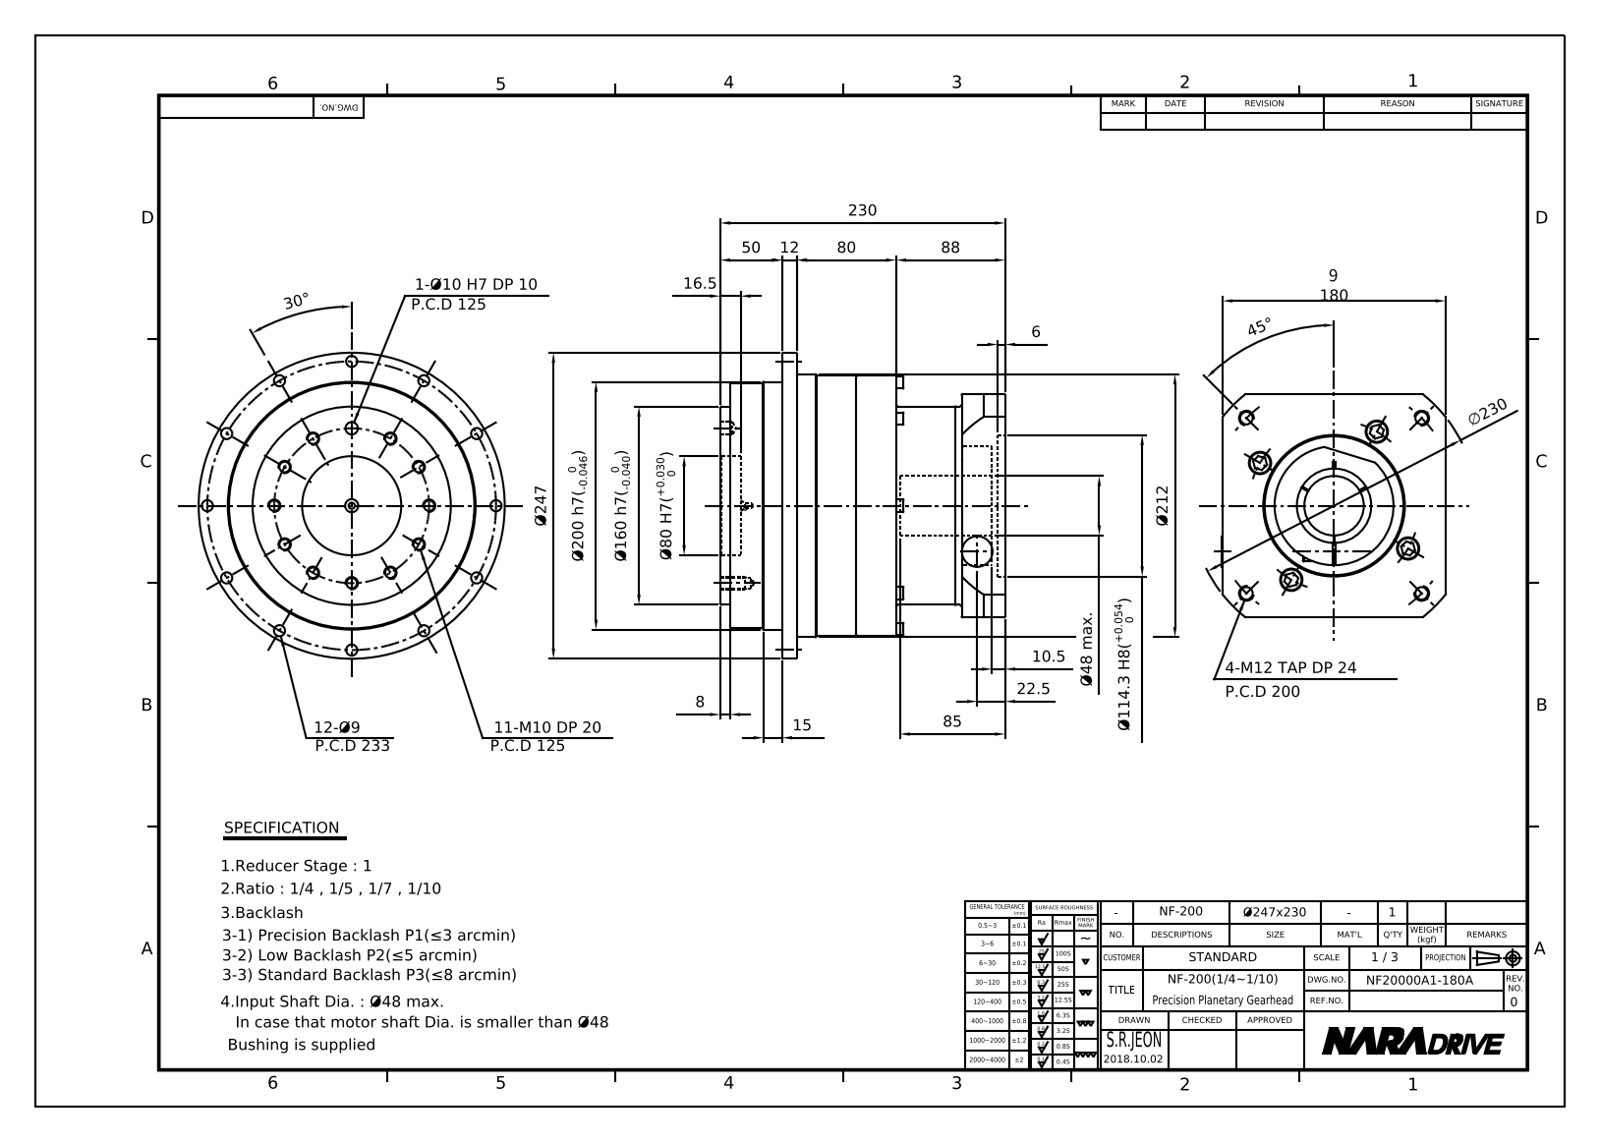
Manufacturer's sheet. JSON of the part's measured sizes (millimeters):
{"part_name": "NF20000A1-180A", "step_written_by": "Autodesk Inventor 2015 (AUTOMOTIVE_DESIGN)", "units": "millimeters", "bodies": {"solids": 1, "faces": 436, "planar": 186, "cylindrical": 127, "other": 123}, "overall_size": [247, 247, 230], "volume_mm3": 5312000, "surface_area_mm2": 463081, "round_holes": [[8.38, 12], [9, 12], [4.92, 8], [6.5, 8], [10.11, 8], [14, 4], [20, 4], [10, 1], [11, 1], [12.5, 1], [14.5, 1], [48, 1]], "round_bosses_or_shafts": [[10, 9], [6, 8], [18, 4], [12, 4], [247, 1], [212, 1], [210, 1], [200, 1]], "partial_cylinders_radius": [[2, 4], [9, 1], [115, 1]], "face_to_face_distances": [180, 43, 134, 179, 120, 85, 25, 60, 1, 91], "hole_center_spacings": [62.5, 100.98, 157.35, 69.76, 116.5, 132.21, 173.47, 32.35]}
